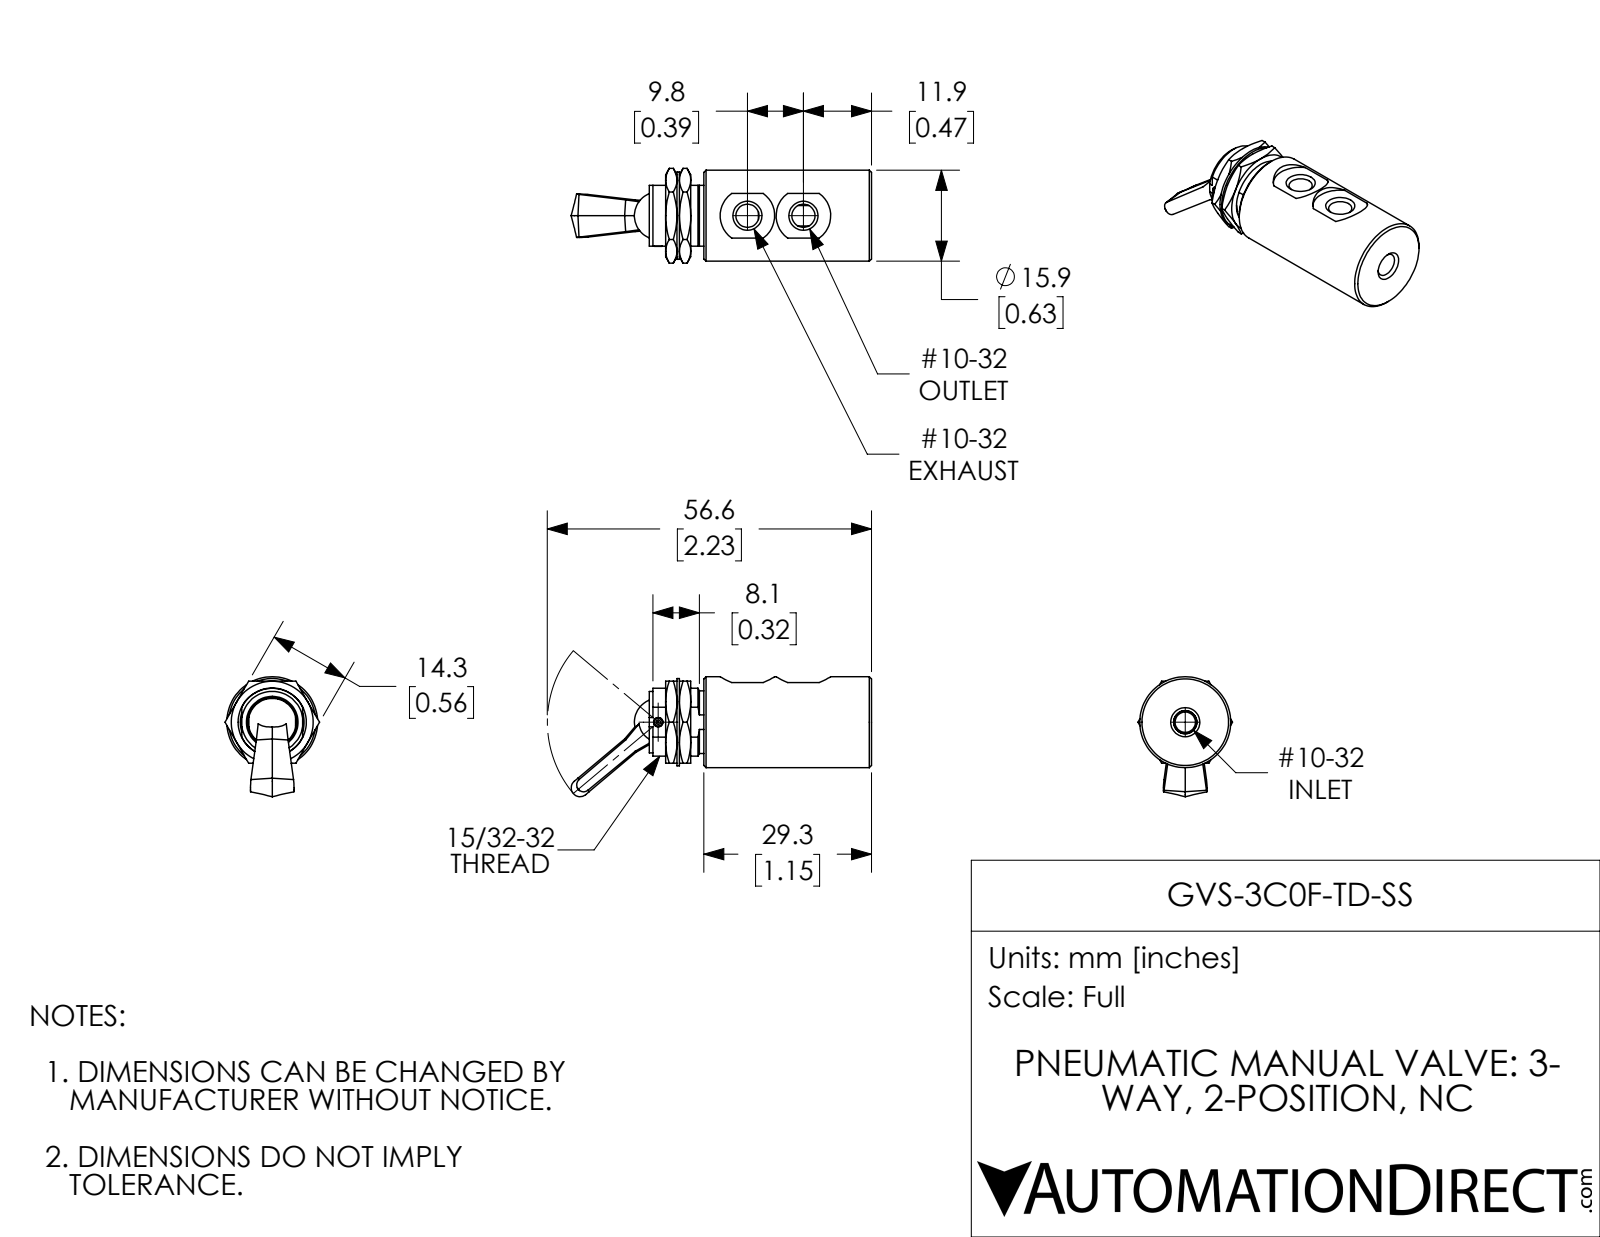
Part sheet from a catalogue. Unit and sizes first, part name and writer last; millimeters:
Units: millimetres
Overall size (bounding box): 52.5 × 20.9 × 16.5
Round holes (diameter × count): ⌀4 ×3, ⌀0.8 ×1, ⌀1.6 ×1, ⌀1.8 ×1, ⌀3.6 ×1, ⌀5 ×1, ⌀5.8 ×1, ⌀8.6 ×1, ⌀11.1 ×1
Round bosses / shafts (diameter × count): ⌀15.9 ×1, ⌀15.2 ×1, ⌀10.9 ×1, ⌀10.7 ×1, ⌀1.6 ×1
Partial cylindrical surfaces — rounded edges, fillets, slot ends (radius × count): R4.8 ×2, R5.9 ×1, R6.1 ×1, R6.6 ×1
Main face-to-face distances: 34, 33.5, 0.4, 2, 2.4, 29.3, 4.3, 4.7, 14.3, 3
Hole centre spacings: 9.8
Volume: 6 330 mm³ · Surface area: 4 283 mm²
Bodies: 6 solids, 255 faces (93 planar, 91 cylindrical, 71 other)
Part name (STEP PRODUCT): GVS-3C0F-TD-SS
STEP written by: SolidWorks 2018 (AUTOMOTIVE_DESIGN)
